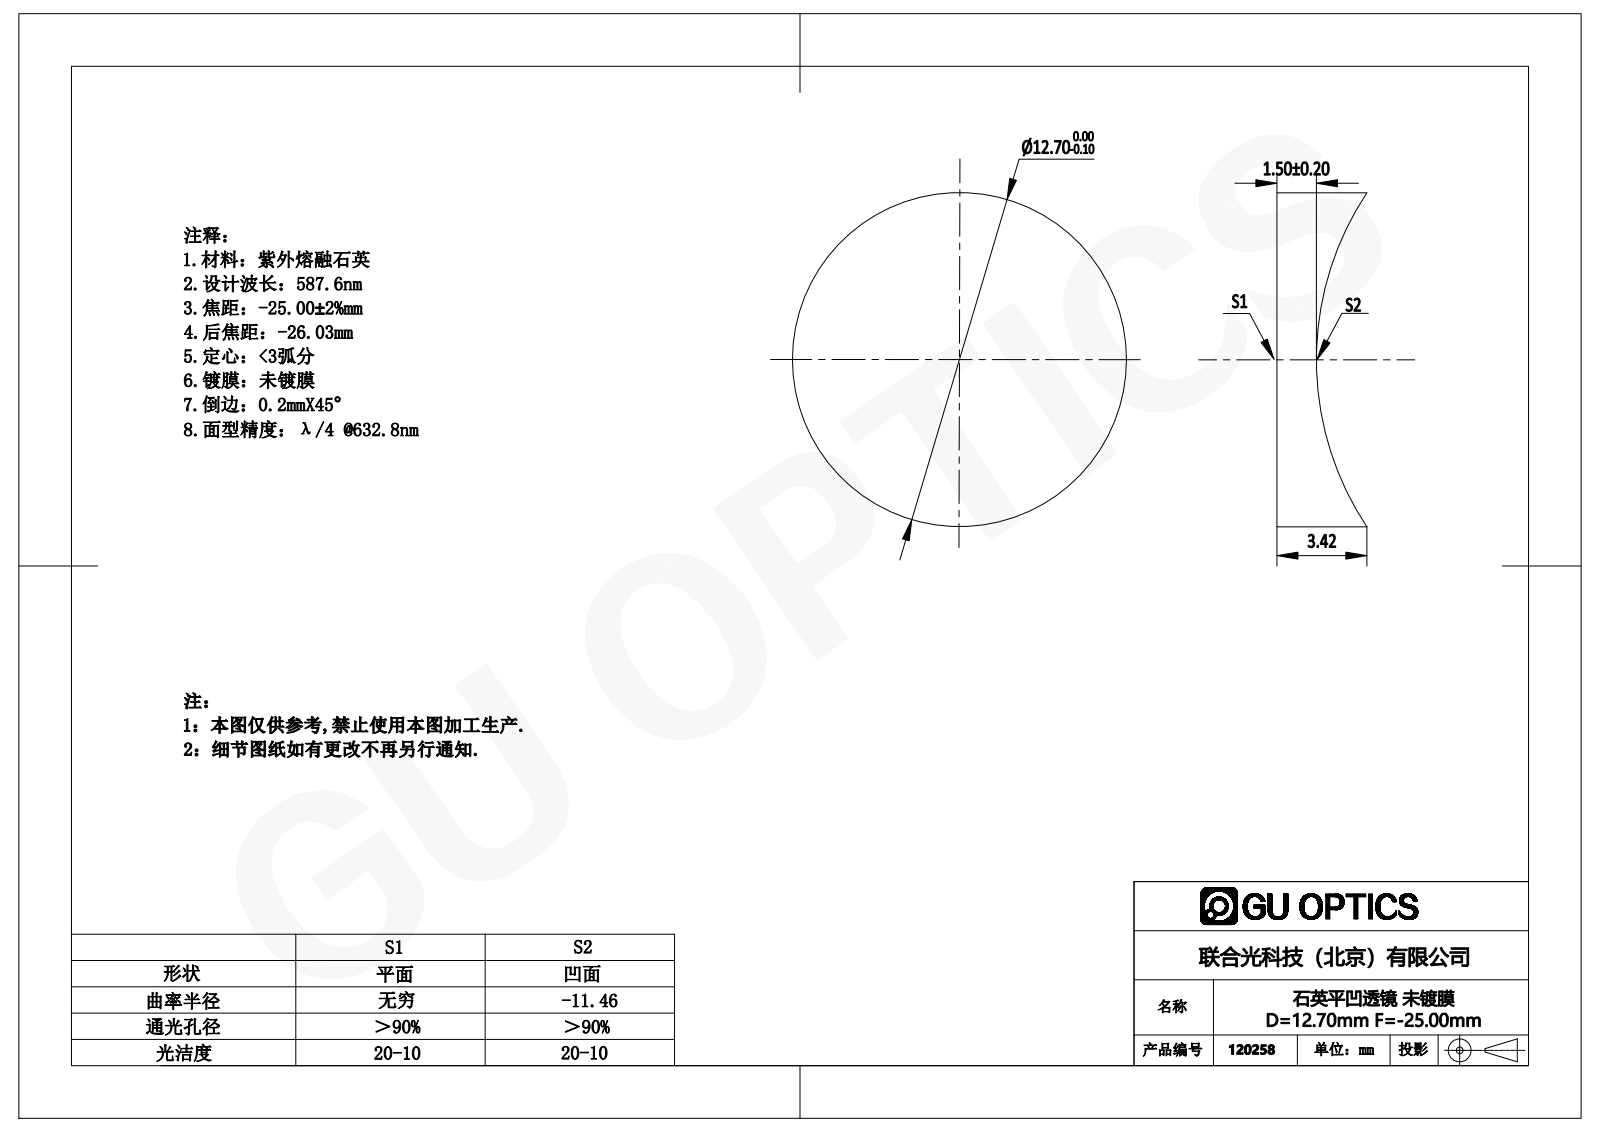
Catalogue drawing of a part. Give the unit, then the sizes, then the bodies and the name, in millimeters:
Units: millimetres
Overall size (bounding box): 12.7 × 12.7 × 3.42
Round bosses / shafts (diameter × count): ⌀12.7 ×1
Volume: 308 mm³ · Surface area: 401 mm²
Bodies: 1 solid, 5 faces (1 planar, 2 cylindrical, 2 other)
Part name (STEP PRODUCT): 120258
STEP written by: SolidWorks 2016 (AUTOMOTIVE_DESIGN)
